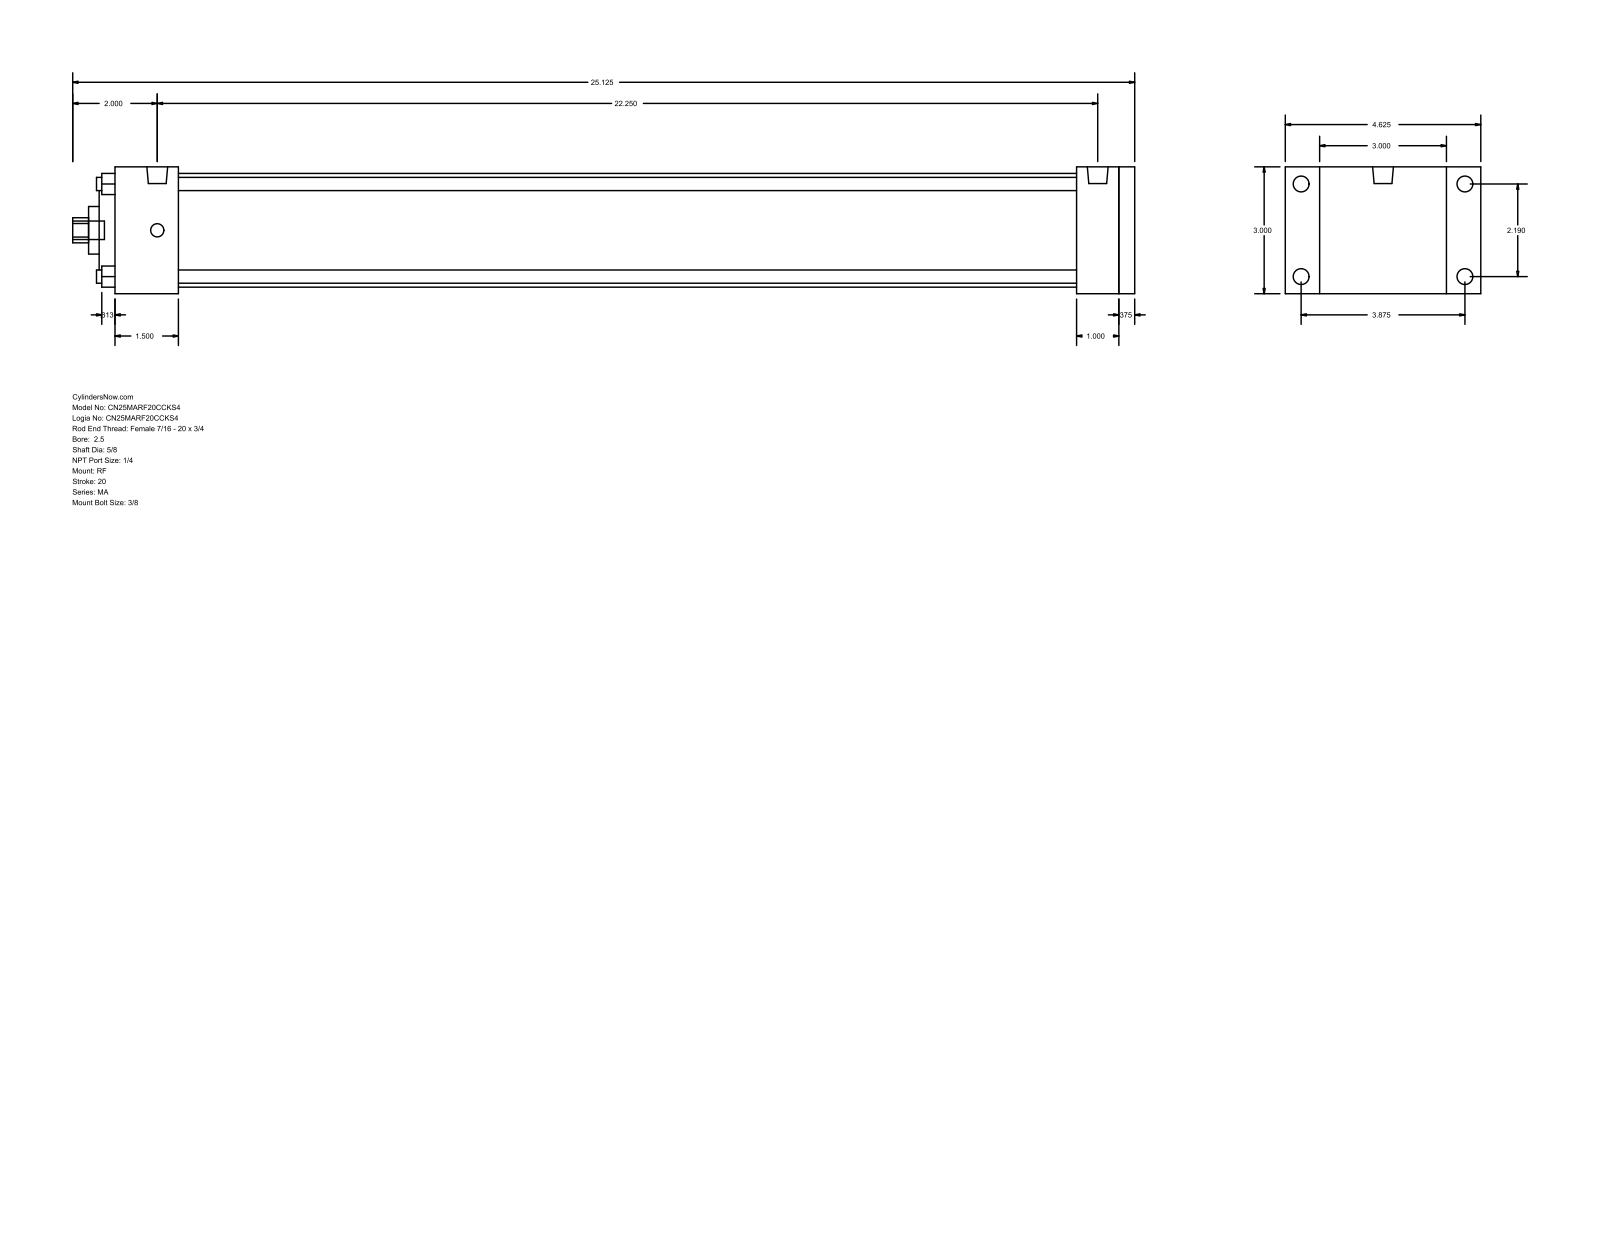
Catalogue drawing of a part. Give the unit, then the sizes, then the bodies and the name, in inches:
Units: inches
Overall size (bounding box): 25.125 × 4.625 × 3
Round holes (diameter × count): ⌀0.313 ×4, ⌀0.625 ×1, ⌀1.125 ×1, ⌀2 ×1, ⌀2.69 ×1
Round bosses / shafts (diameter × count): ⌀0.375 ×4, ⌀0.313 ×4, ⌀0.492 ×2, ⌀0.437 ×1
Partial cylindrical surfaces — rounded edges, fillets, slot ends (radius × count): R0.297 ×1
Main face-to-face distances: 3, 24.125, 0.375, 23.75, 1, 1.5, 22.75, 21.25, 22.25, 22.625
Hole centre spacings: 1.548, 2.19, 3.097
Bodies: 0 solids, 94 faces (65 planar, 29 cylindrical, 0 other)
Part name (STEP PRODUCT): MA_RF__0250_0.625
STEP written by: GSSL Pune (CONFIG_CONTROL_DESIGN)
